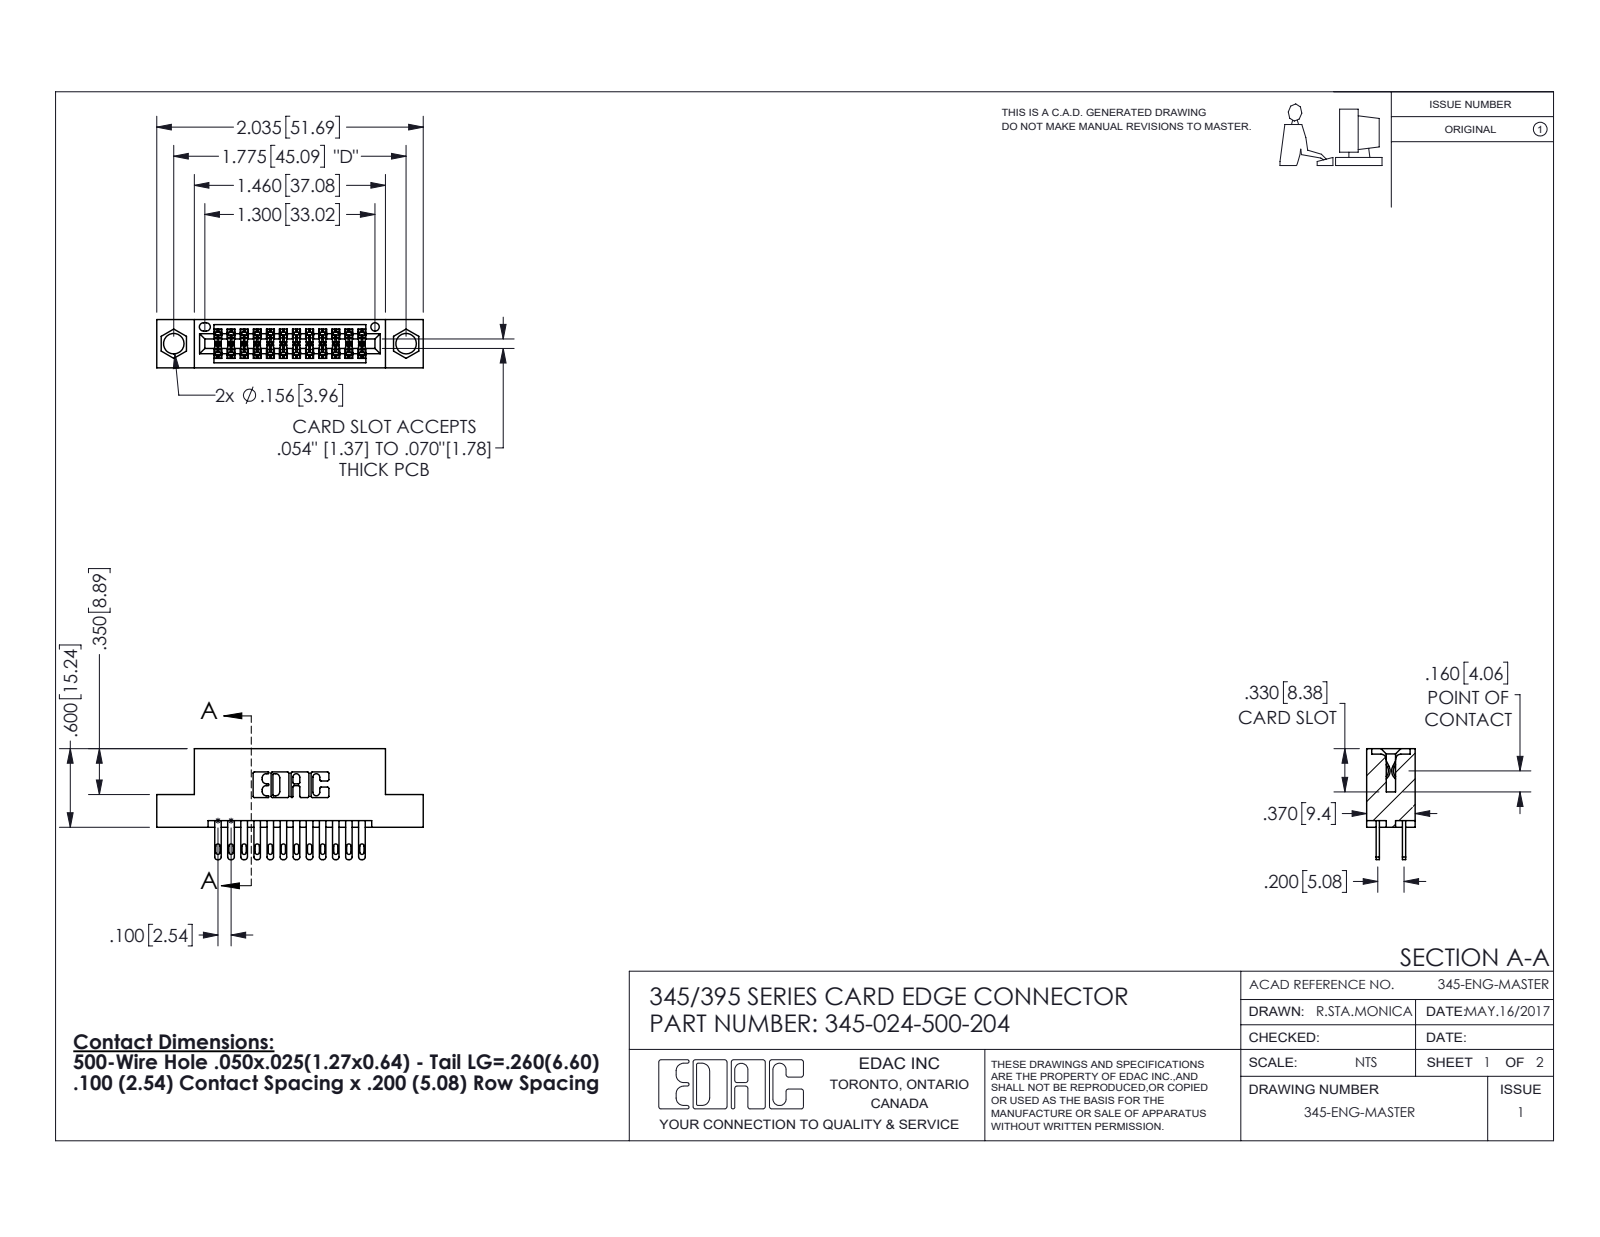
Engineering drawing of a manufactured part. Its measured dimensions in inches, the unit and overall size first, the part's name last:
Units: inches
Overall size (bounding box): 2.035 × 0.847 × 0.37
Round holes (diameter × count): ⌀0.156 ×2, ⌀0.064 ×1
Partial cylindrical surfaces — rounded edges, fillets, slot ends (radius × count): R0.006 ×36, R0.016 ×24, R0.02 ×24, R0.01 ×22, R0.007 ×6, R0.031 ×6, R0.026 ×3, R0.014 ×2
Main face-to-face distances: 0.2, 0.298, 0.072, 0.098, 0.272, 0.025, 0.37, 0.225, 0.1, 0.175
Hole centre spacings: 0.27, 1.543, 1.775
Volume: 0.287 in³ · Surface area: 10.04 in²
Bodies: 25 solids, 1244 faces (742 planar, 502 cylindrical, 0 other)
Part name (STEP PRODUCT): 345-292-001_345-293-100; 345 Part_Flush Mounting Lugs - 0.156 Dia-TI; 345-024-500-204
STEP written by: SolidWorks 2020 (CONFIG_CONTROL_DESIGN)
